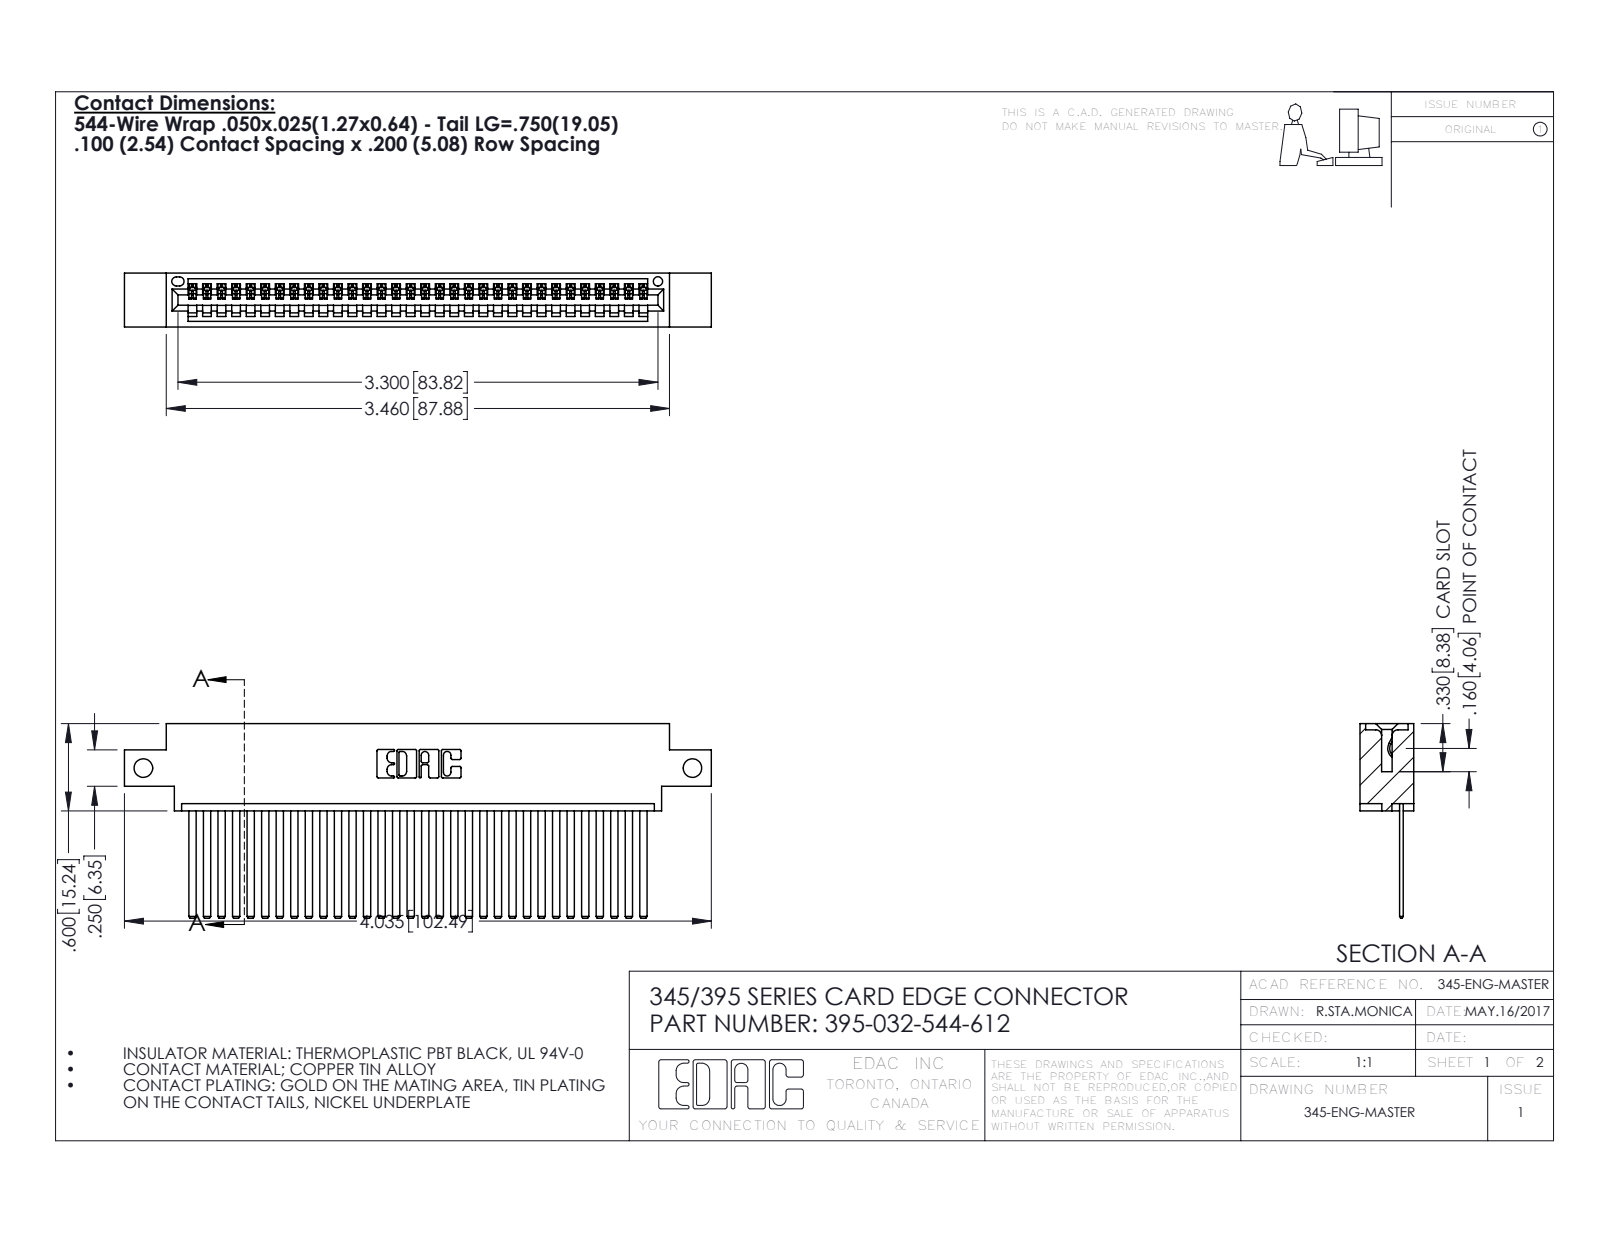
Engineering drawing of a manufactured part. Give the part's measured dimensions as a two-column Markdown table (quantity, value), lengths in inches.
| quantity | value |
| --- | --- |
| part name | 345-292-001_345-293-144; 345 Part_0.170 Offset - Side Mount; 395-032-544-612 |
| STEP written by | SolidWorks 2016 (CONFIG_CONTROL_DESIGN) |
| units | inches |
| bodies | 33 solids, 1794 faces (1236 planar, 558 cylindrical, 0 other) |
| overall size | 4.035 × 1.337 × 0.37 |
| volume | 0.599 in³ |
| surface area | 21.72 in² |
| round holes (diameter × count) | 0.128 × 2, 0.064 × 1 |
| partial cylindrical surfaces (radius × count) | 0.006 × 64, 0.01 × 22, 0.007 × 6, 0.031 × 6, 0.026 × 3, 0.031 × 2, 0.04 × 2, 0.014 × 1 |
| main face-to-face distances | 0.072, 0.298, 0.025, 0.098, 0.272, 0.37, 0.2, 0.225, 0.175, 0.149 |
| hole center spacings | 3.775 |
